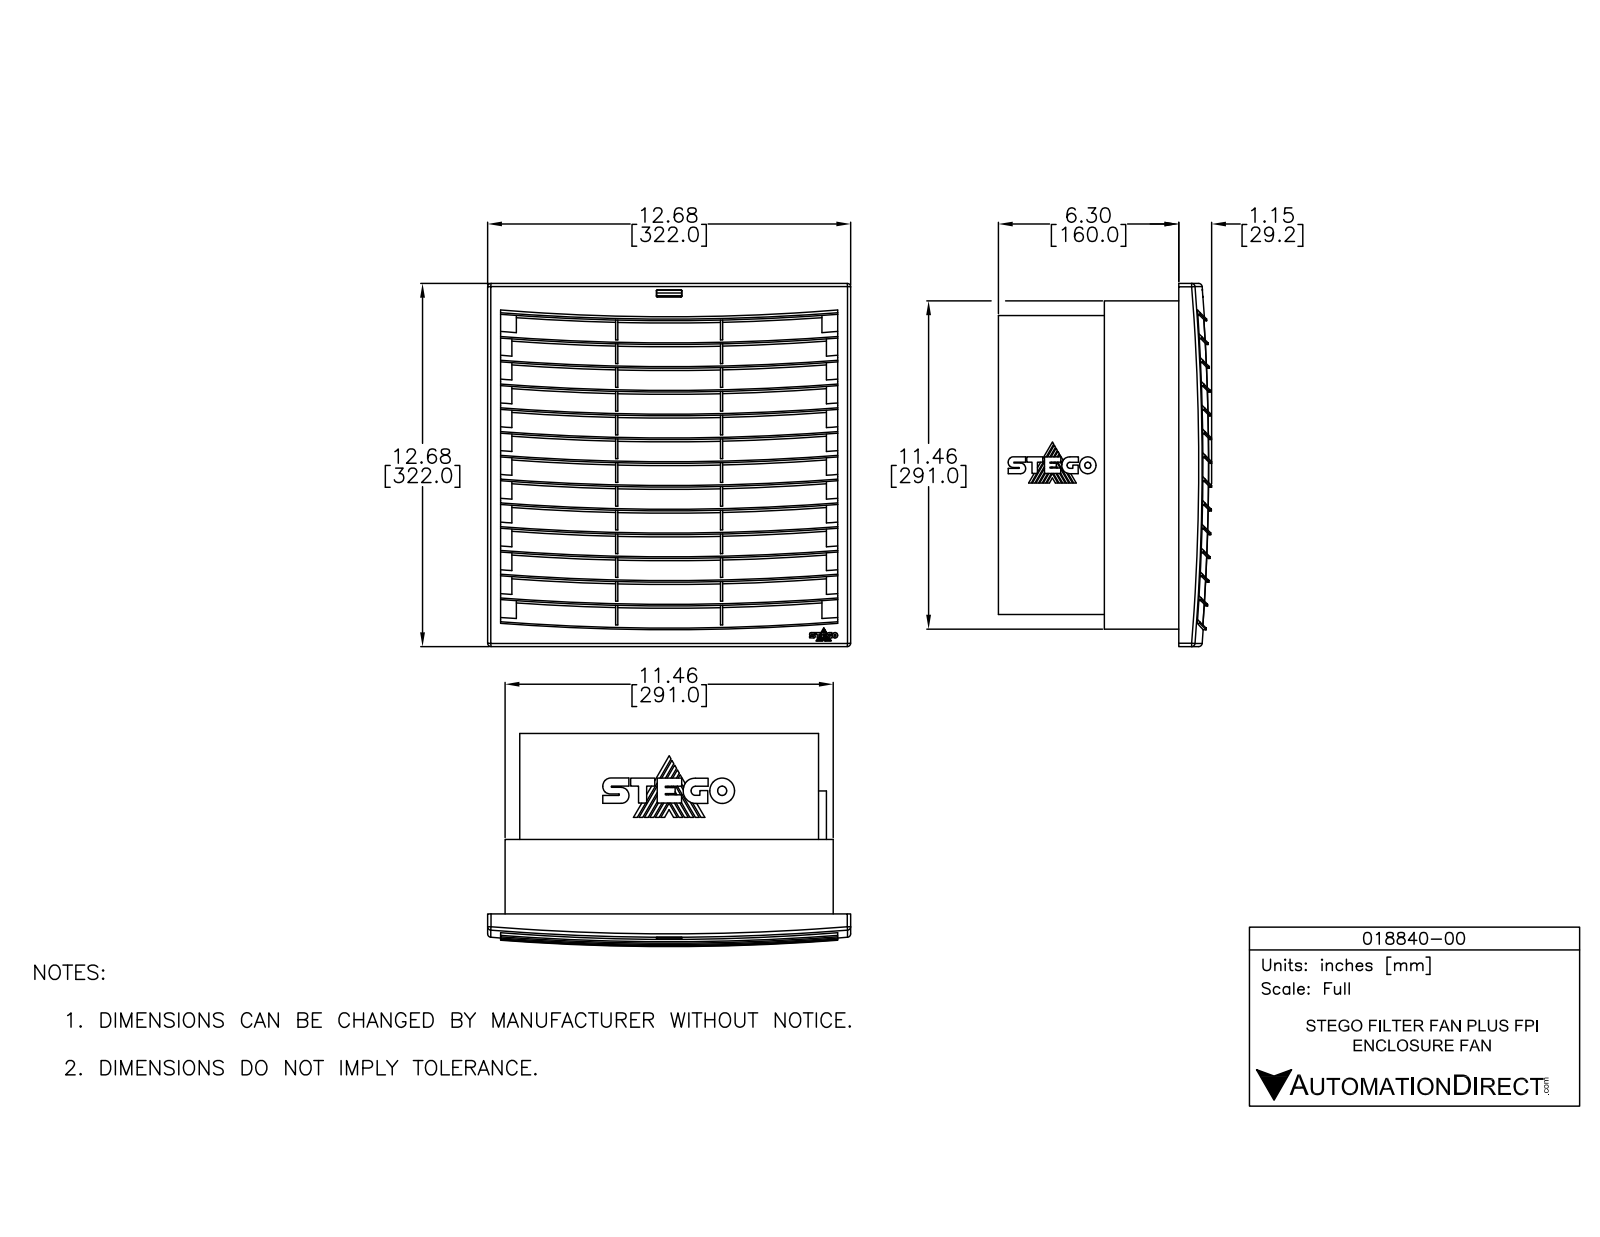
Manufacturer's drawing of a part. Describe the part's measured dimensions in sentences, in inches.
The part is named "018840-00". Its 3-D file was written by "SolidWorks 2018 (AUTOMOTIVE_DESIGN)". It is 1 solid with 860 faces: 506 planar, 354 cylindrical and 0 other. Overall it measures 12.677 by 12.677 by 7.441 inches. Its volume is 283.7 cubic inches and its surface area 1 629 square inches. Round holes: 1 of diameter 3, 1 of diameter 3.99, 1 of diameter 4.692, 1 of diameter 4.979, 1 of diameter 5.909, 1 of diameter 5.969, 1 of diameter 6.958, 1 of diameter 7.126, 1 of diameter 7.947, 1 of diameter 8.344, 1 of diameter 9.134, 1 of diameter 9.738. Round bosses or shafts: 1 of diameter 11.389, 1 of diameter 10.846, 1 of diameter 10.738, 1 of diameter 8.698, 1 of diameter 8.341, 1 of diameter 7.481, 1 of diameter 7.352, 1 of diameter 6.362. Partial cylindrical surfaces (rounded edges, fillets, slot ends): 23 of radius 64.96, 7 of radius 4.43, 4 of radius 0.276, 4 of radius 0.343, 1 of radius 1.217, 1 of radius 1.737, 1 of radius 1.914, 1 of radius 44.216. The main face-to-face distances are 0.059, 0.27, 0.636, 1.272, 1.909, 0.541, 2.545, 0.197, 0.811, 3.181.
